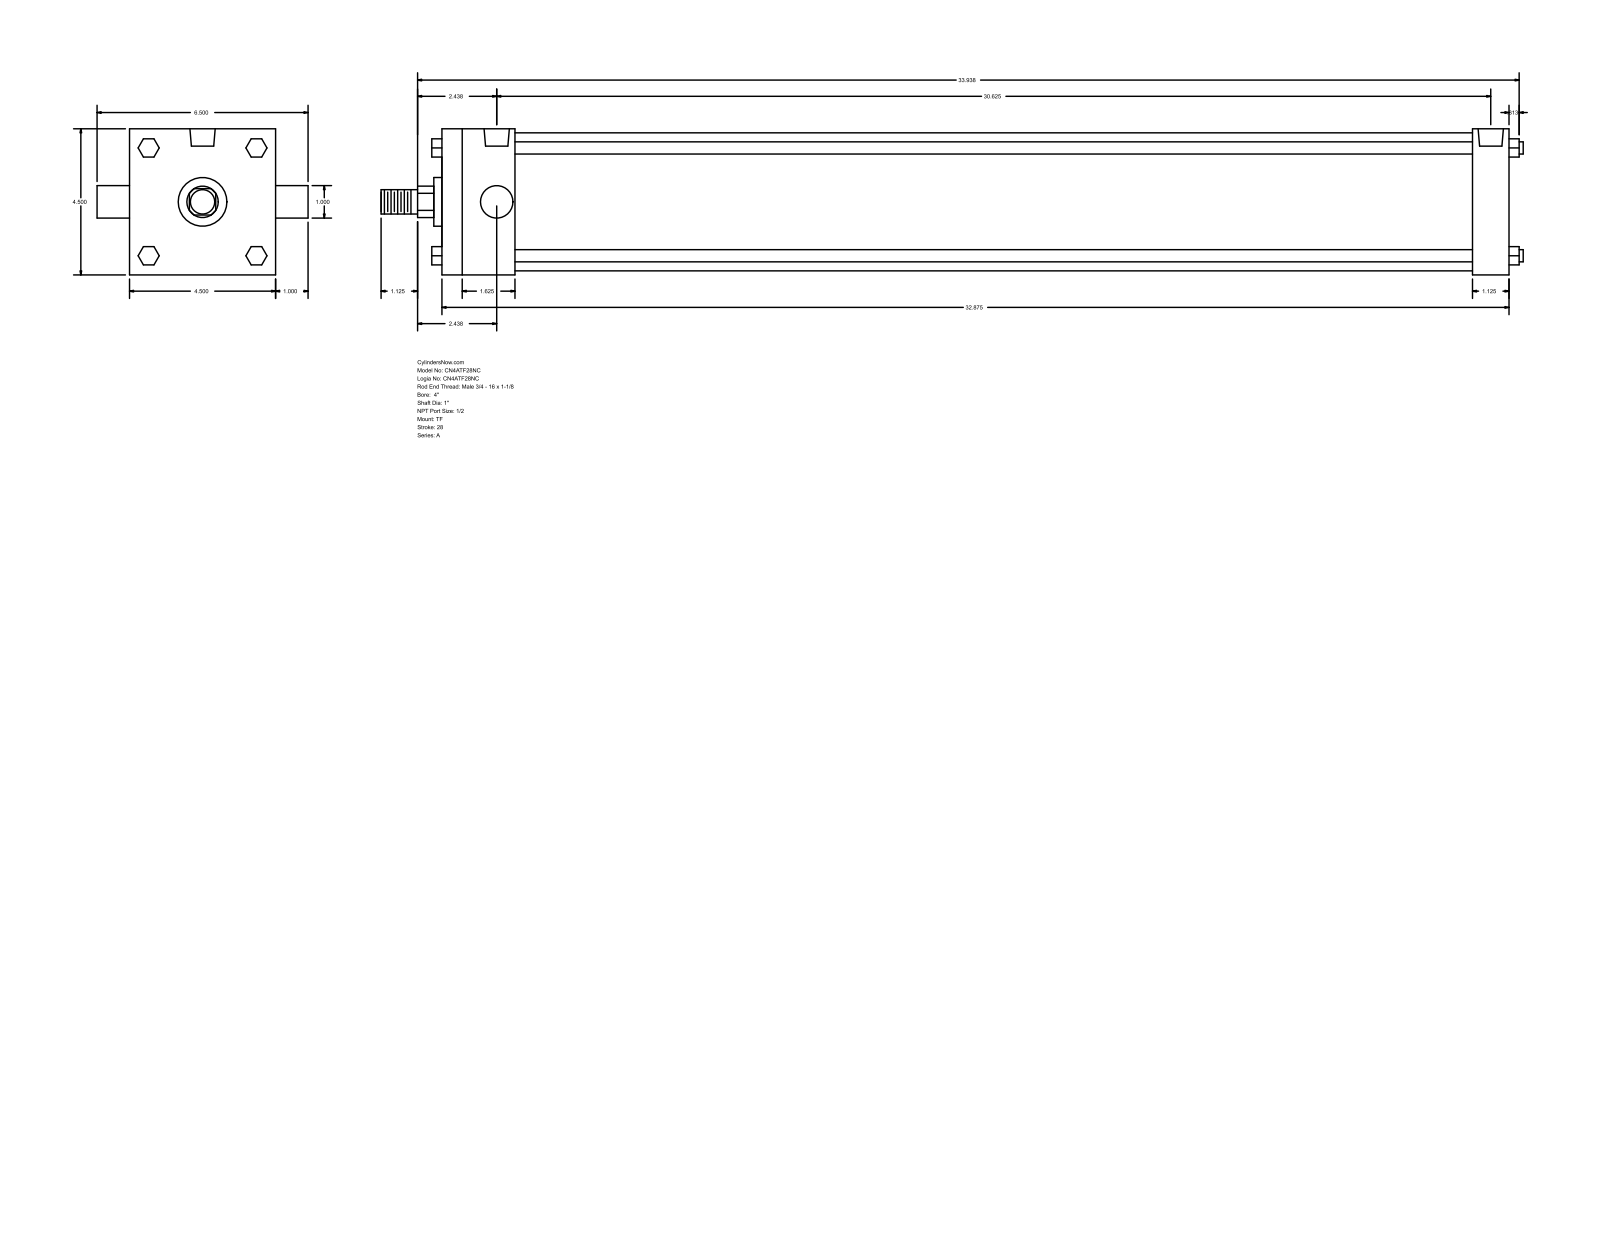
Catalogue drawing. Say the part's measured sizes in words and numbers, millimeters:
The part is named "A_TF__0400_1". Its 3-D file was written by "GSSL Pune (CONFIG_CONTROL_DESIGN)". It is 0 solids with 120 faces: 92 planar, 28 cylindrical and 0 other. Overall it measures 893.76 by 165.1 by 114.3 millimeters. Round holes: 3 of diameter 8.73, 2 of diameter 19.77. Round bosses or shafts: 4 of diameter 9.53, 2 of diameter 25.4, 1 of diameter 107.95, 1 of diameter 38.1, 1 of diameter 19.05. Partial cylindrical surfaces (rounded edges, fillets, slot ends): 1 of radius 12.29. The main face-to-face distances are 114.3, 835.03, 806.45, 28.58, 57.15, 749.3, 777.88, 14.29, 42.16, 73.03. The hole center spacings are 3.18, 774.7, 771.52, 777.88.
